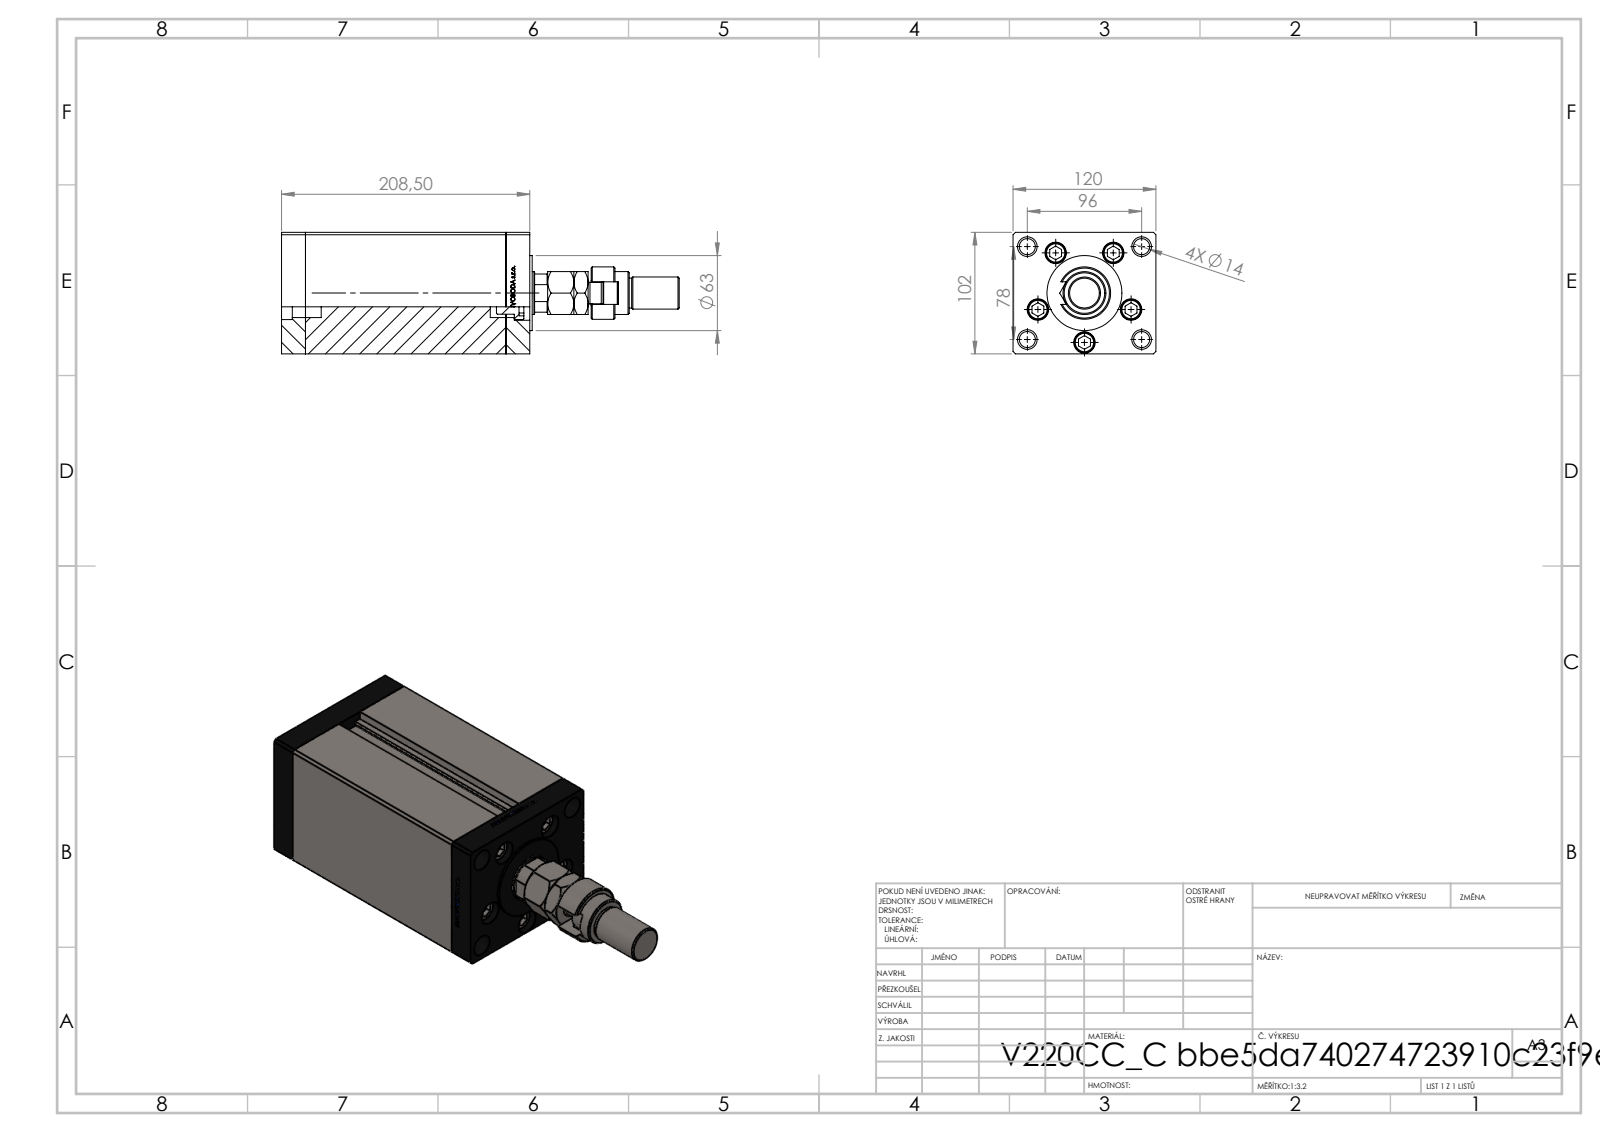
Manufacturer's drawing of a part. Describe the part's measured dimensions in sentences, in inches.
The part is named "MFA; V220C FRONT; V220C_C MIDDLE; V220C_VC_C (+3 more)". Its 3-D file was written by "SolidWorks 2019 (CONFIG_CONTROL_DESIGN)". It is 15 solids with 1250 faces: 570 planar, 174 cylindrical and 506 other. Overall it measures 13.15 by 4.724 by 4.016 inches. Its volume is 136.7 cubic inches and its surface area 495.3 square inches. Round holes: 9 of diameter 0.531, 5 of diameter 0.709, 4 of diameter 0.472, 4 of diameter 0.65, 1 of diameter 0.669, 1 of diameter 1.004. Round bosses or shafts: 5 of diameter 0.315, 4 of diameter 0.669, 1 of diameter 2.48, 1 of diameter 1.732, 1 of diameter 1.417, 1 of diameter 1.102, 1 of diameter 1.063, 1 of diameter 0.984. Partial cylindrical surfaces (rounded edges, fillets, slot ends): 2 of radius 0.037, 1 of radius 0.374, 1 of radius 0.591, 1 of radius 0.689. The main face-to-face distances are 4.724, 4.016, 0.787, 6.634, 7.421, 1.348, 8.209, 6.86, 6.073, 0.561. The hole center spacings are 1.634, 2.435, 0.96, 1.051, 1.887, 1.893, 1.962, 2.109.
